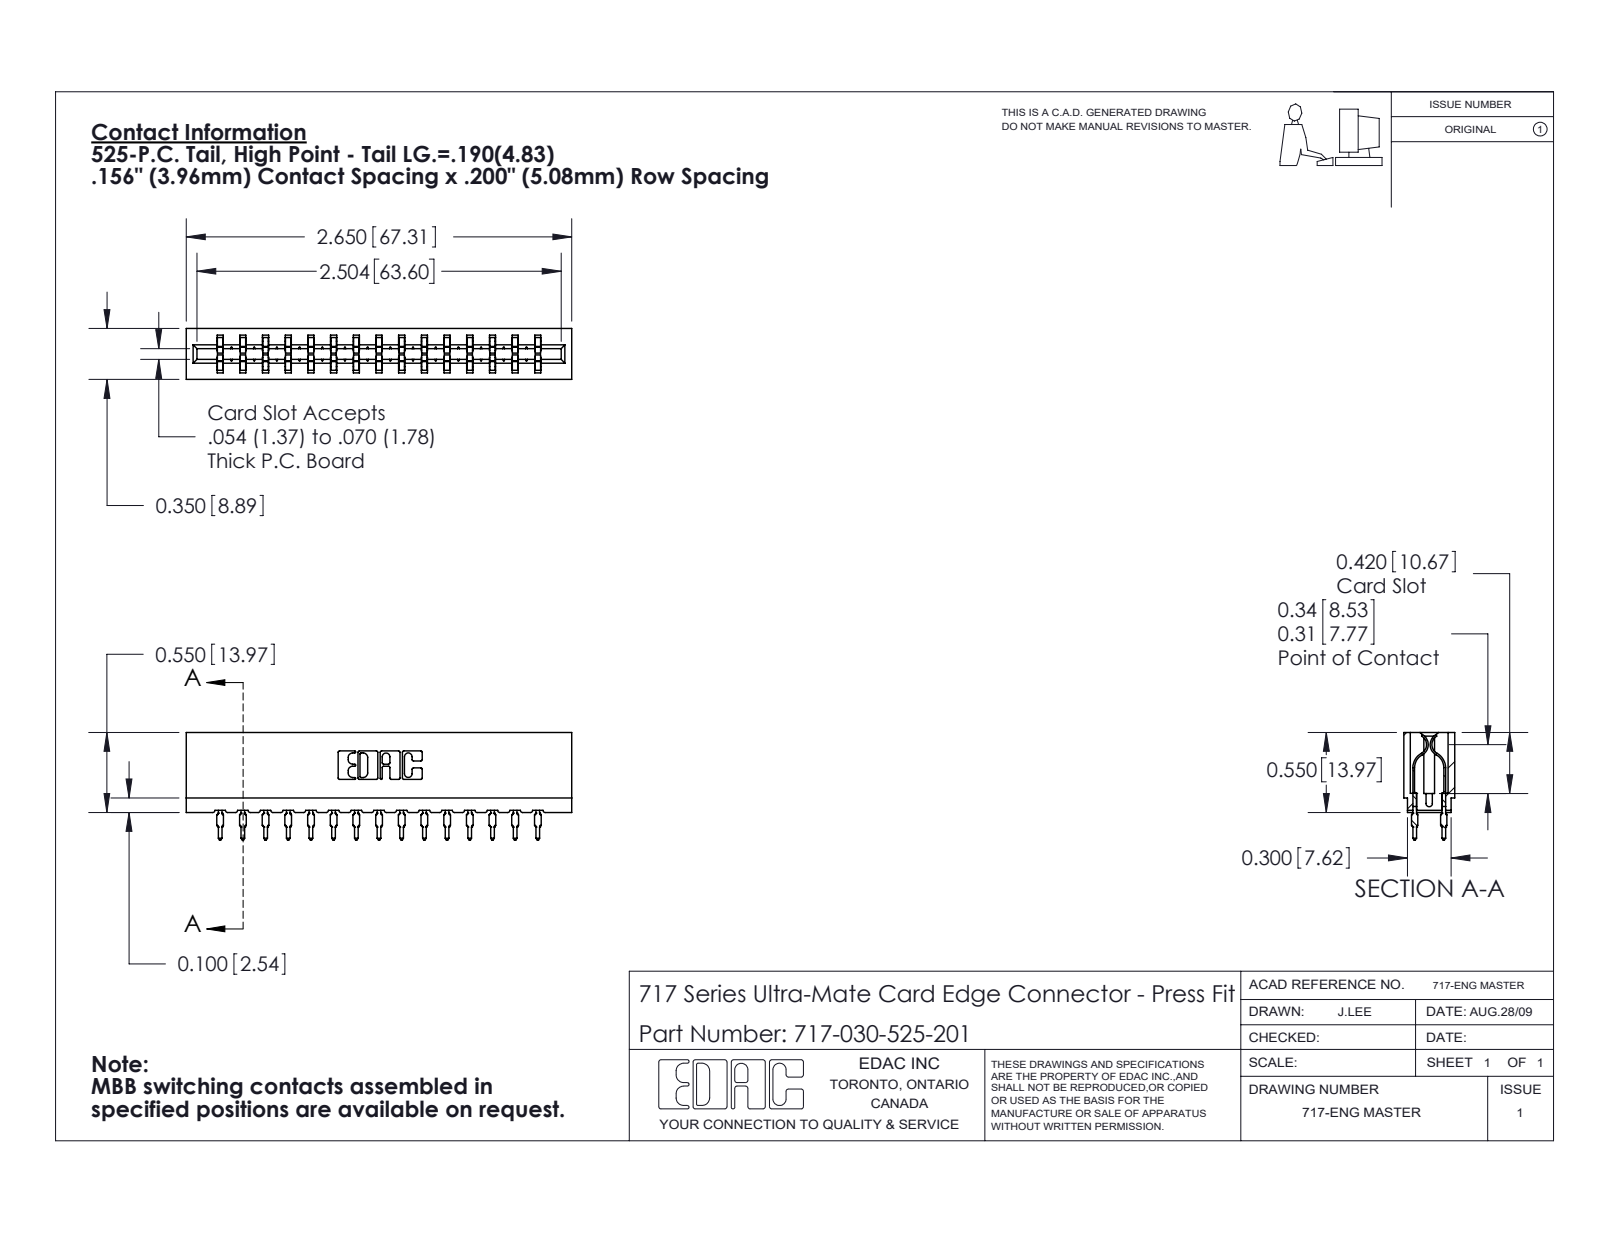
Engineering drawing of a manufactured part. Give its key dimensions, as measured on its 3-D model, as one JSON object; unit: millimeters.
{"part_name": "717-030-525-201; 745-292-001_525; 717 Part_Insulator Option - 06", "step_written_by": "SolidWorks 2020 (CONFIG_CONTROL_DESIGN)", "units": "millimeters", "bodies": {"solids": 31, "faces": 2794, "planar": 1449, "cylindrical": 565, "other": 780}, "overall_size": [67.3, 18.8, 8.9], "volume_mm3": 5930, "surface_area_mm2": 8684, "partial_cylinders_radius": [[0.5, 60], [0.4, 30], [0.3, 22], [0.1, 8], [0.3, 8], [0.2, 6], [0.8, 6], [0.7, 3]], "face_to_face_distances": [5.4, 3.5, 8.9, 4, 15.8, 11.9, 7.9, 1.6, 7.3, 1.9]}
